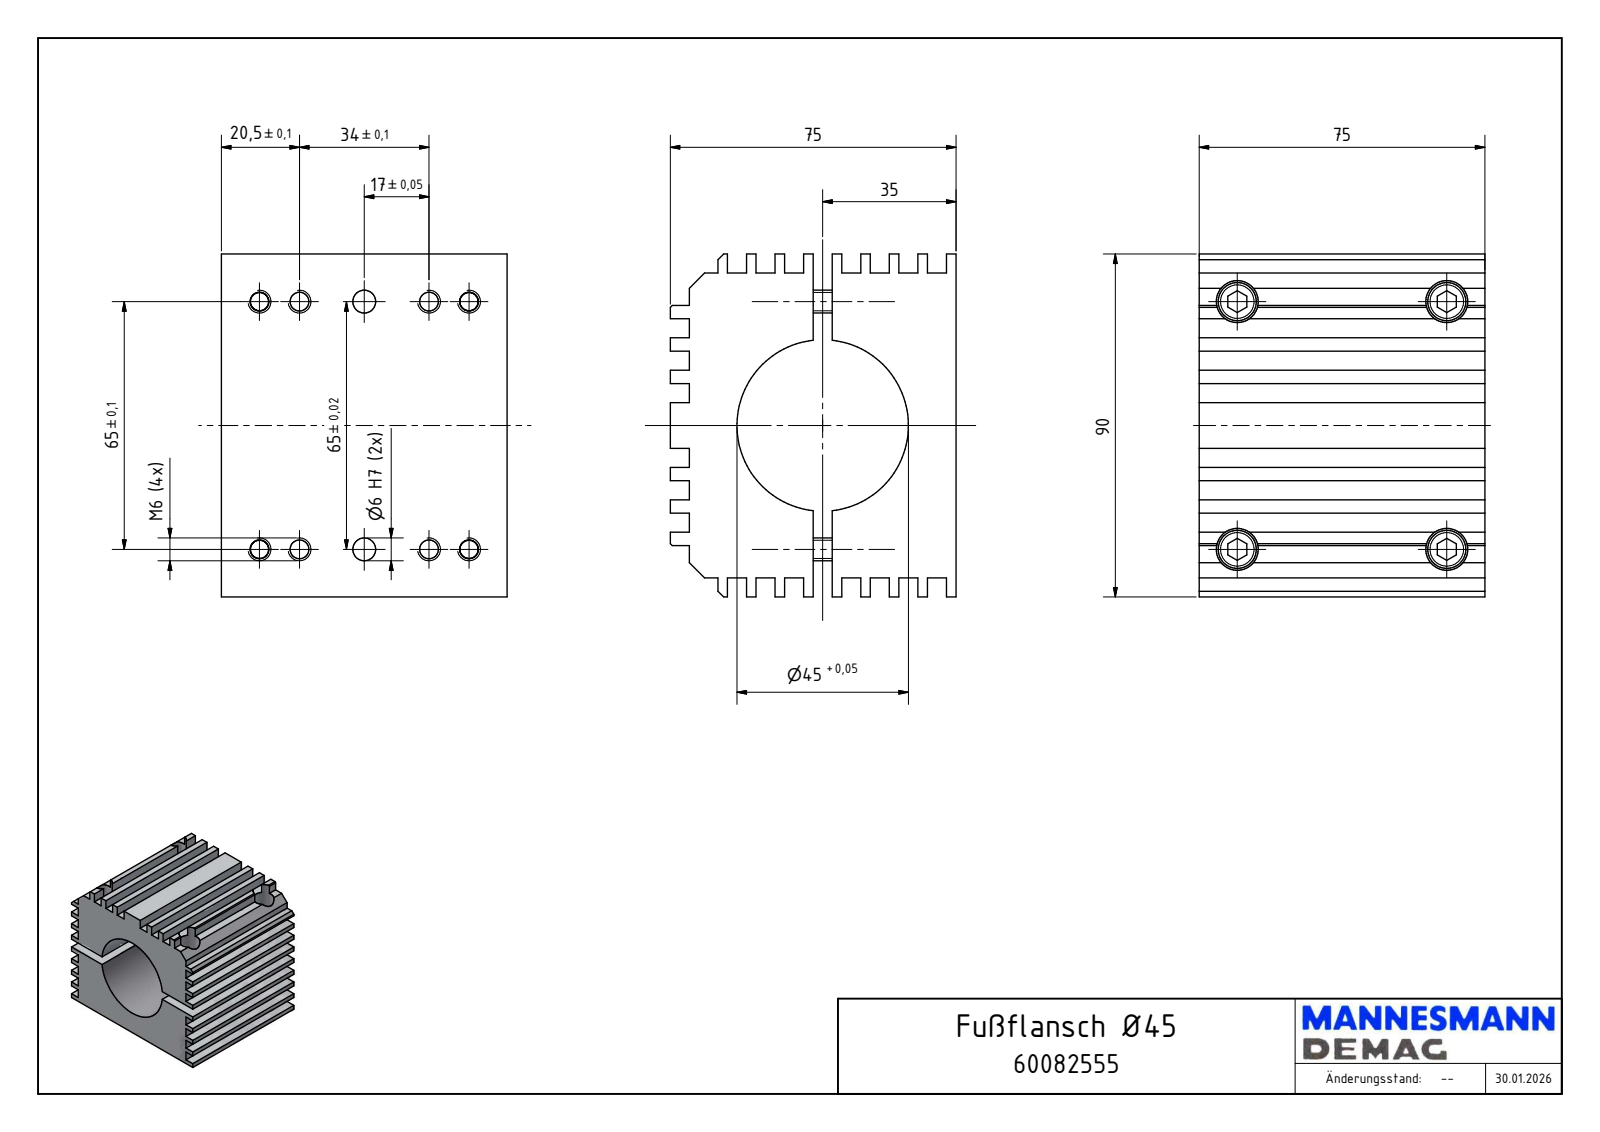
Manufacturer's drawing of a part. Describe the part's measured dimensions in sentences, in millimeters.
The part is named "60082555_Fußflansch Ø45". Its 3-D file was written by "Autodesk Inventor 2024 (AUTOMOTIVE_DESIGN)". It is 1 solid with 208 faces: 168 planar, 28 cylindrical and 12 other. Overall it measures 90 by 75 by 75 millimeters. Its volume is 304 159 cubic millimeters and its surface area 73 208 square millimeters. Round holes: 8 of diameter 4.92, 4 of diameter 6.6, 4 of diameter 11, 2 of diameter 6, 1 of diameter 45. Round bosses or shafts: 4 of diameter 10, 4 of diameter 6. The main face-to-face distances are 5, 37.5, 7.5, 15, 22.5, 30, 32.5, 2.5, 10, 75. The hole center spacings are 65, 10.5, 17, 27.5, 44.5, 65.84, 67.19, 70.58.
